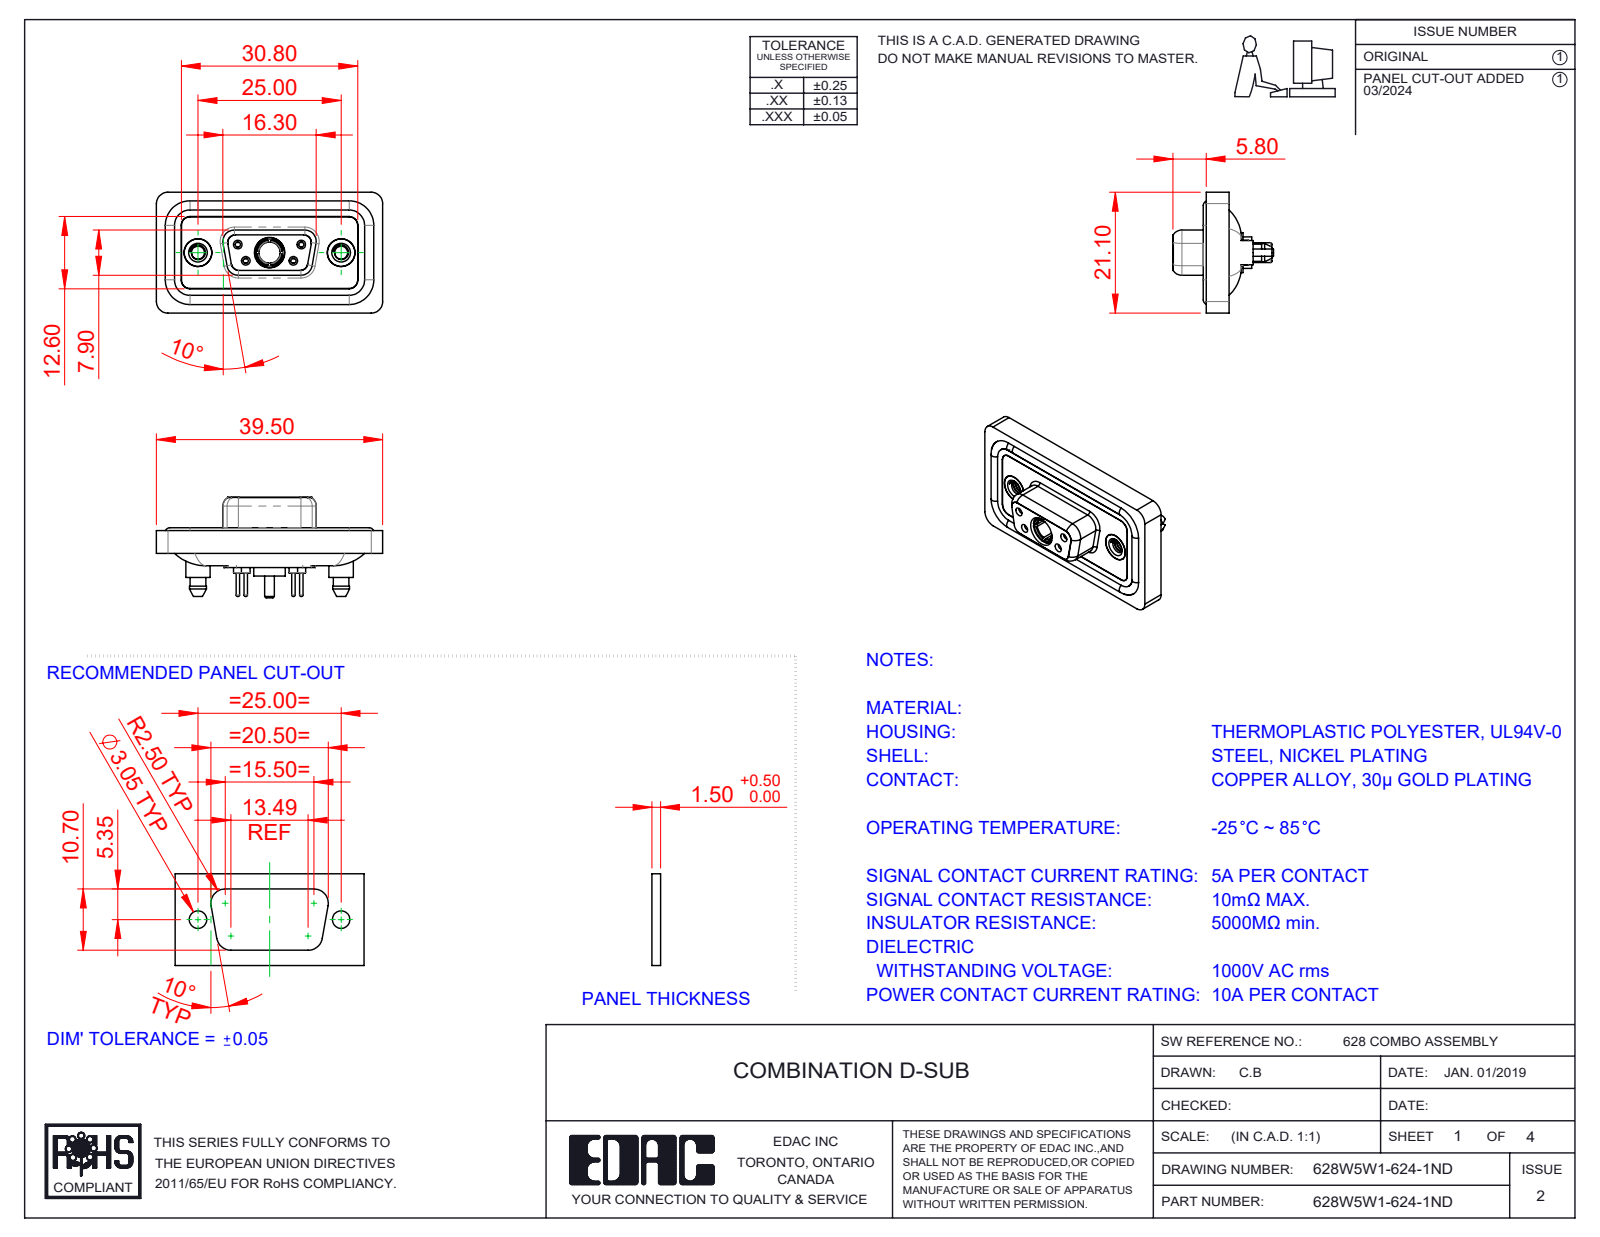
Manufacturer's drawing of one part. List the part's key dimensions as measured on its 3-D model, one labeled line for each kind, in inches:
Part name (STEP PRODUCT): 628Combo Contact Row 1_24; 628Combo Contact Row 2_24; 628Combo Shell Front_09 Contacts; Power Socket_10A S (+5 more)
STEP written by: SolidWorks 2023 (CONFIG_CONTROL_DESIGN)
Units: inches
Bodies: 13 solids, 746 faces (210 planar, 335 cylindrical, 201 other)
Overall size (bounding box): 1.555 × 0.831 × 0.691
Volume: 0.298 in³ · Surface area: 12.34 in²
Round holes (diameter × count): ⌀0.035 ×4, ⌀0.043 ×4, ⌀0.059 ×4, ⌀0.079 ×4, ⌀0.191 ×3, ⌀0.063 ×2, ⌀0.067 ×2, ⌀0.089 ×2, ⌀0.157 ×2, ⌀0.159 ×2, ⌀0.197 ×2, ⌀0.146 ×1
Round bosses / shafts (diameter × count): ⌀0.063 ×6, ⌀0.087 ×4, ⌀0.024 ×4, ⌀0.213 ×2, ⌀0.195 ×2, ⌀0.189 ×2, ⌀0.167 ×2, ⌀0.217 ×1
Partial cylindrical surfaces — rounded edges, fillets, slot ends (radius × count): R0.059 ×24, R0.079 ×18, R0.063 ×10, R0.053 ×8, R0.01 ×4, R0.02 ×4, R0.024 ×4, R0.026 ×4
Main face-to-face distances: 0.016, 0.114, 0.071, 0.043, 0.063, 0.02, 0.222, 0.293, 0.211, 0.142
Hole centre spacings: 0.124, 0.225, 0.28, 0.492, 0.713, 0.173, 0.173, 0.327
